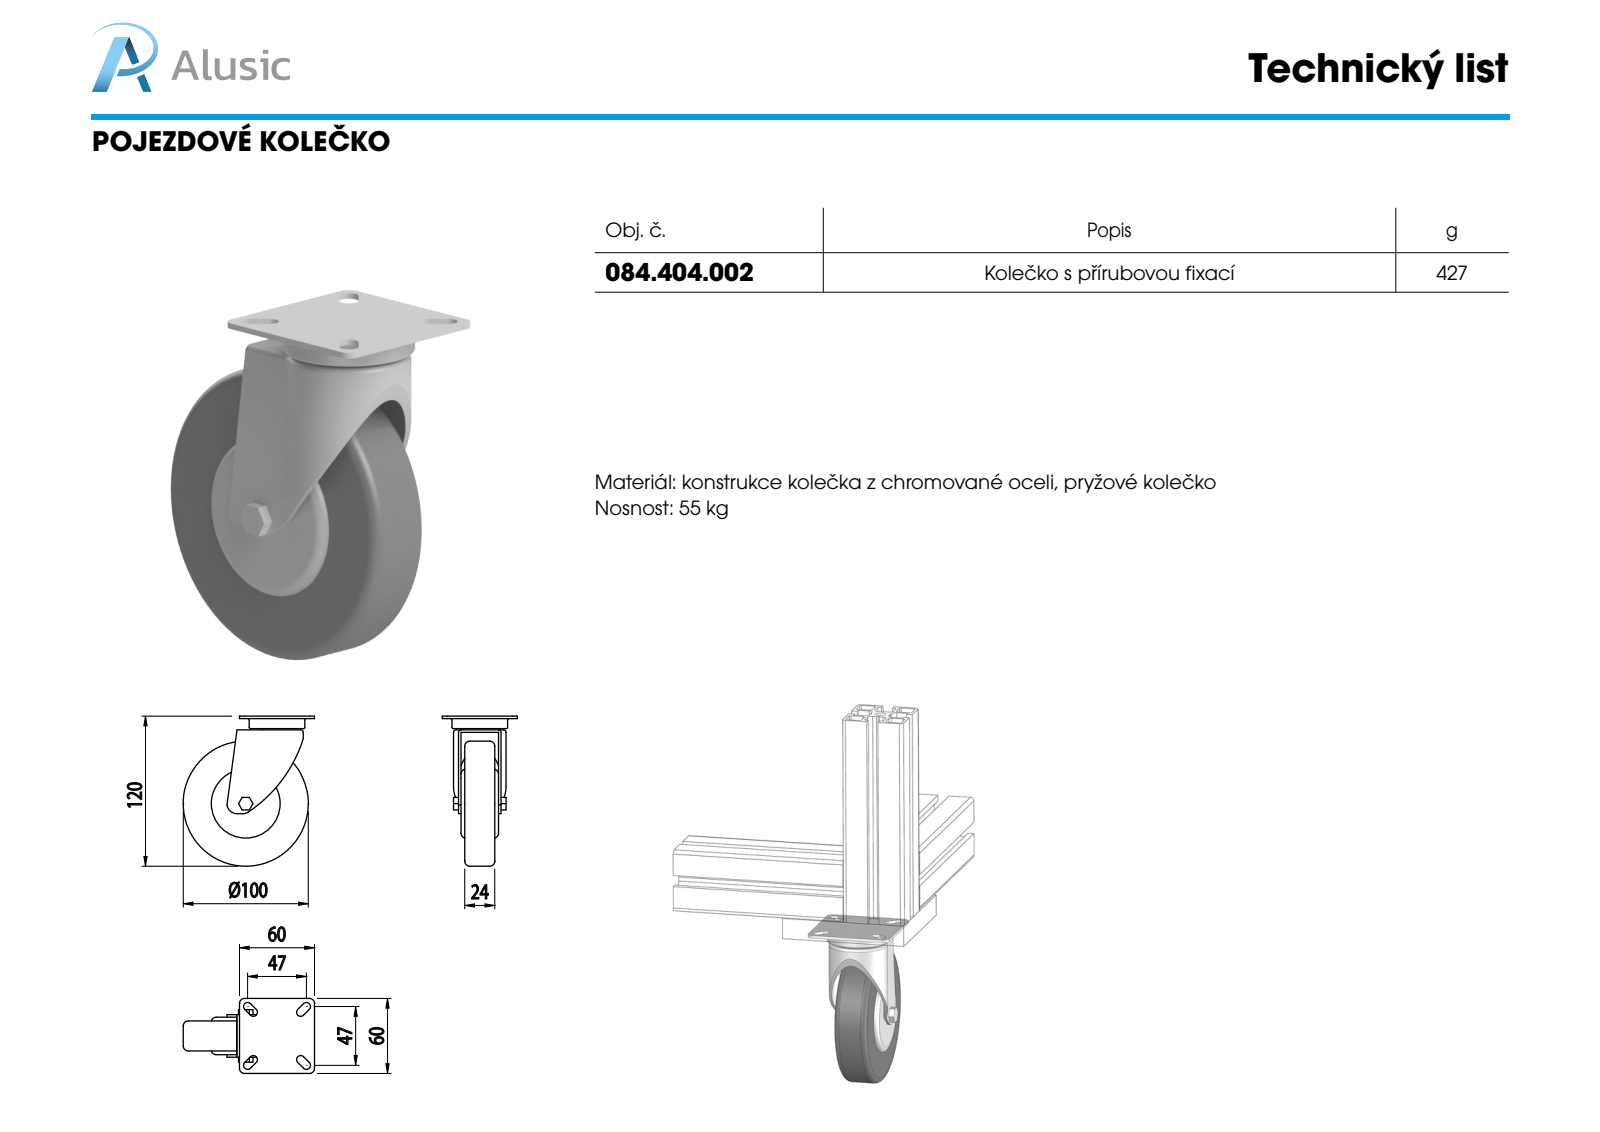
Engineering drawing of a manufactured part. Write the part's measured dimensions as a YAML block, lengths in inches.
part_name: "084.404.002"
step_written_by: "SolidWorks 2011 (CONFIG_CONTROL_DESIGN)"
units: inches
bodies: {solids: 7, faces: 96, planar: 46, cylindrical: 35, other: 15}
overall_size: [4.724, 4.134, 2.362]
volume: 14.31
surface_area: 88.26
round_bosses_or_shafts:
  - {diameter: 3.937, count: 1}
  - {diameter: 1.752, count: 1}
partial_cylinders:
  - {radius: 0.128, count: 8}
  - {radius: 0.157, count: 4}
  - {radius: 0.315, count: 4}
  - {radius: 0.079, count: 2}
  - {radius: 0.394, count: 2}
  - {radius: 0.748, count: 1}
  - {radius: 0.827, count: 1}
  - {radius: 4.331, count: 1}
face_to_face_distances: [0.945, 0.118, 1.063, 0.079, 0.433, 1.181, 0.197, 1.142, 1.26, 0.354]
